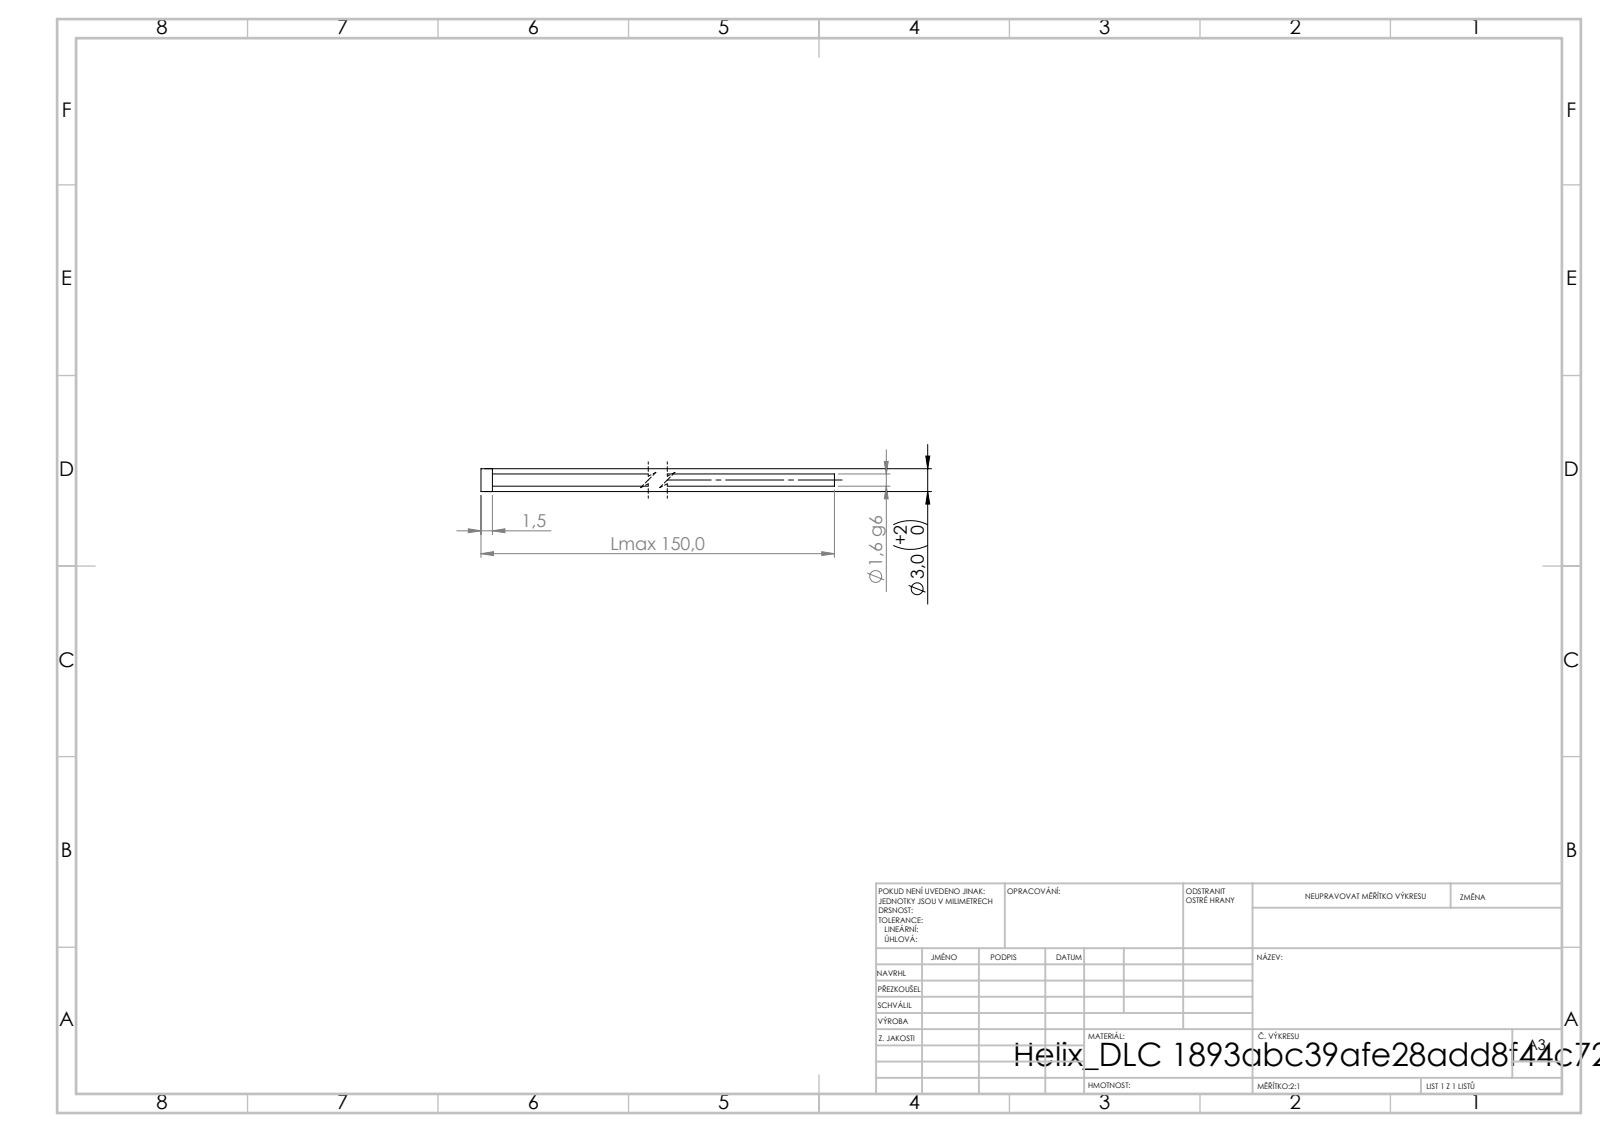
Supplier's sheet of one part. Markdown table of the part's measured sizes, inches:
| quantity | value |
| --- | --- |
| STEP written by | SolidWorks 2019 (CONFIG_CONTROL_DESIGN) |
| units | inches |
| bodies | 1 solid, 16 faces (6 planar, 9 cylindrical, 1 other) |
| overall size | 5.906 × 0.118 × 0.118 |
| volume | 0.021 in³ |
| surface area | 1.47 in² |
| round bosses / shafts (diameter × count) | 0.118 × 1, 0.063 × 1, 0.05 × 1 |
| main face-to-face distances | 0.059, 5.906, 5.846, 3.665, 3.606, 2.241, 3.652, 3.593, 0.013, 2.253 |
